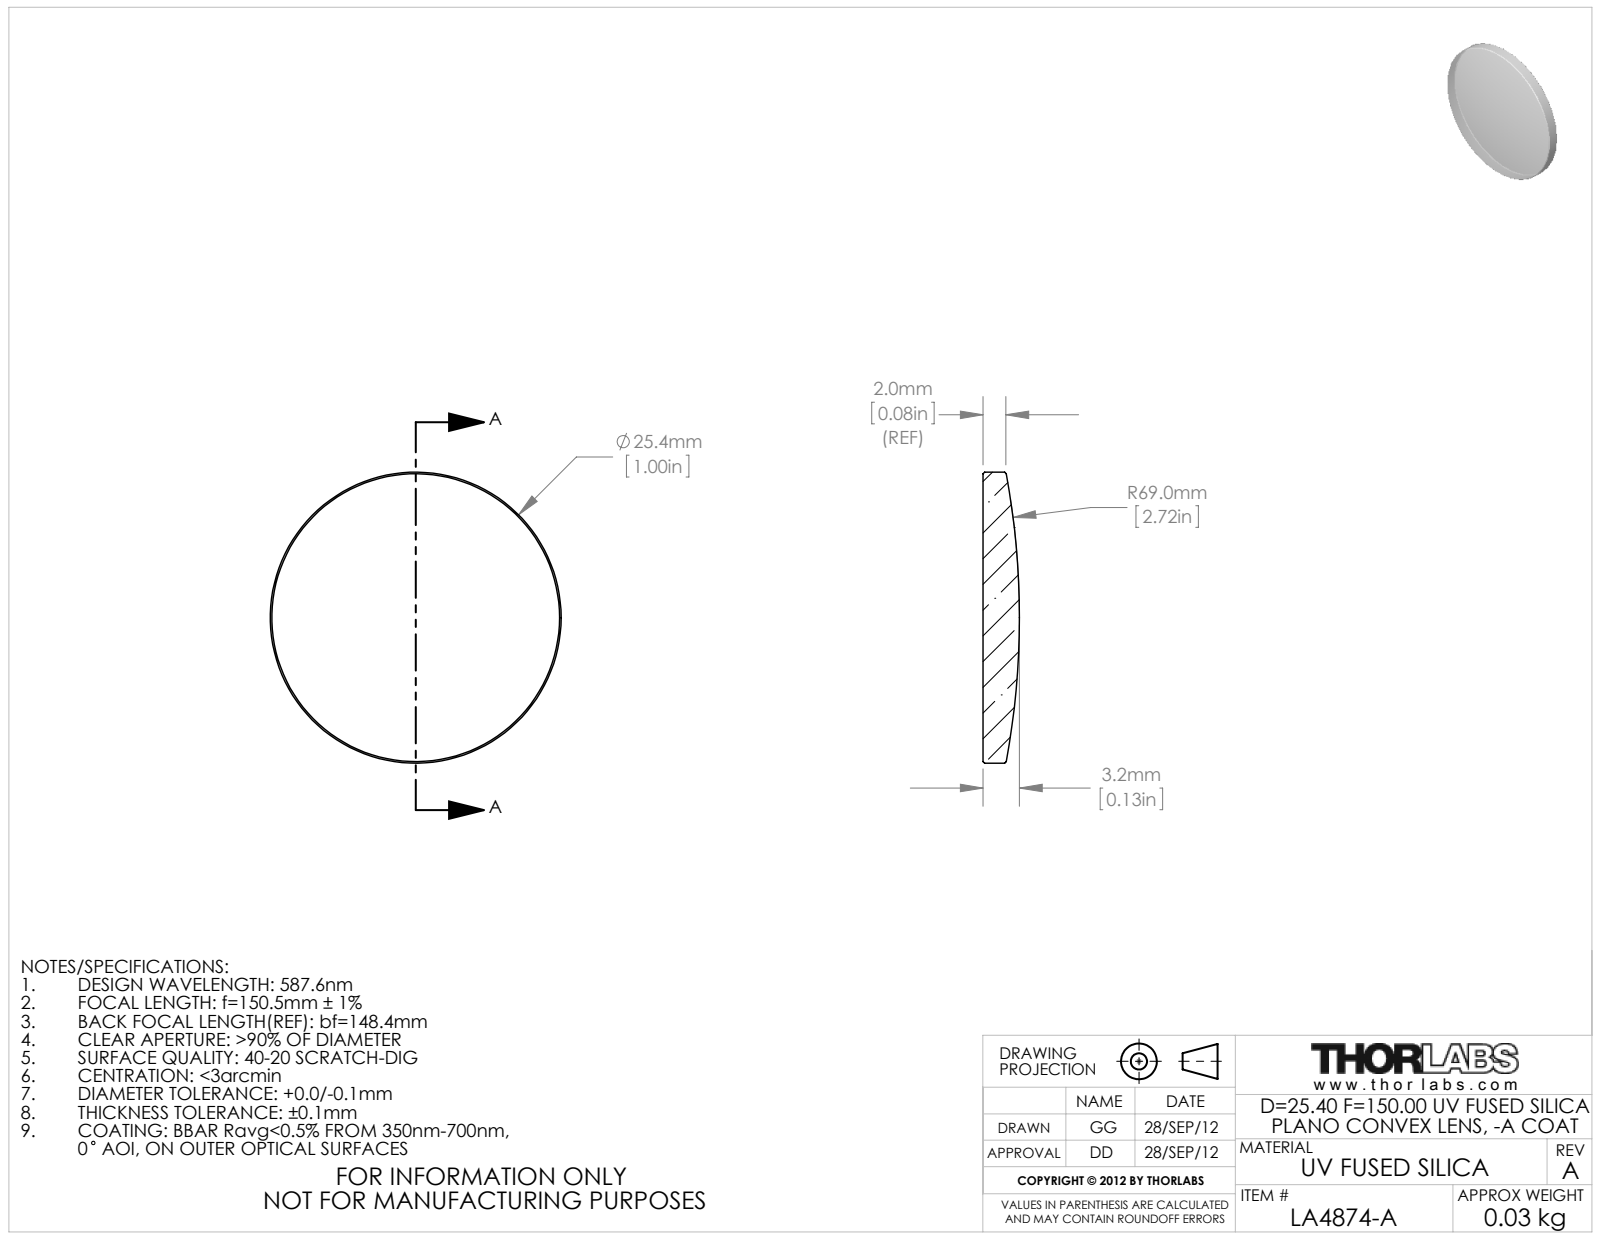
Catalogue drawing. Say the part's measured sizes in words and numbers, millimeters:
The part is named "24990-E0W". Its 3-D file was written by "SolidWorks 2011 (CONFIG_CONTROL_DESIGN)". It is 1 solid with 9 faces: 1 planar, 2 cylindrical and 6 other. Overall it measures 25.4 by 25.4 by 3.18 millimeters. Its volume is 1 312 cubic millimeters and its surface area 1 166 square millimeters. Round bosses or shafts: 1 of diameter 25.4.
